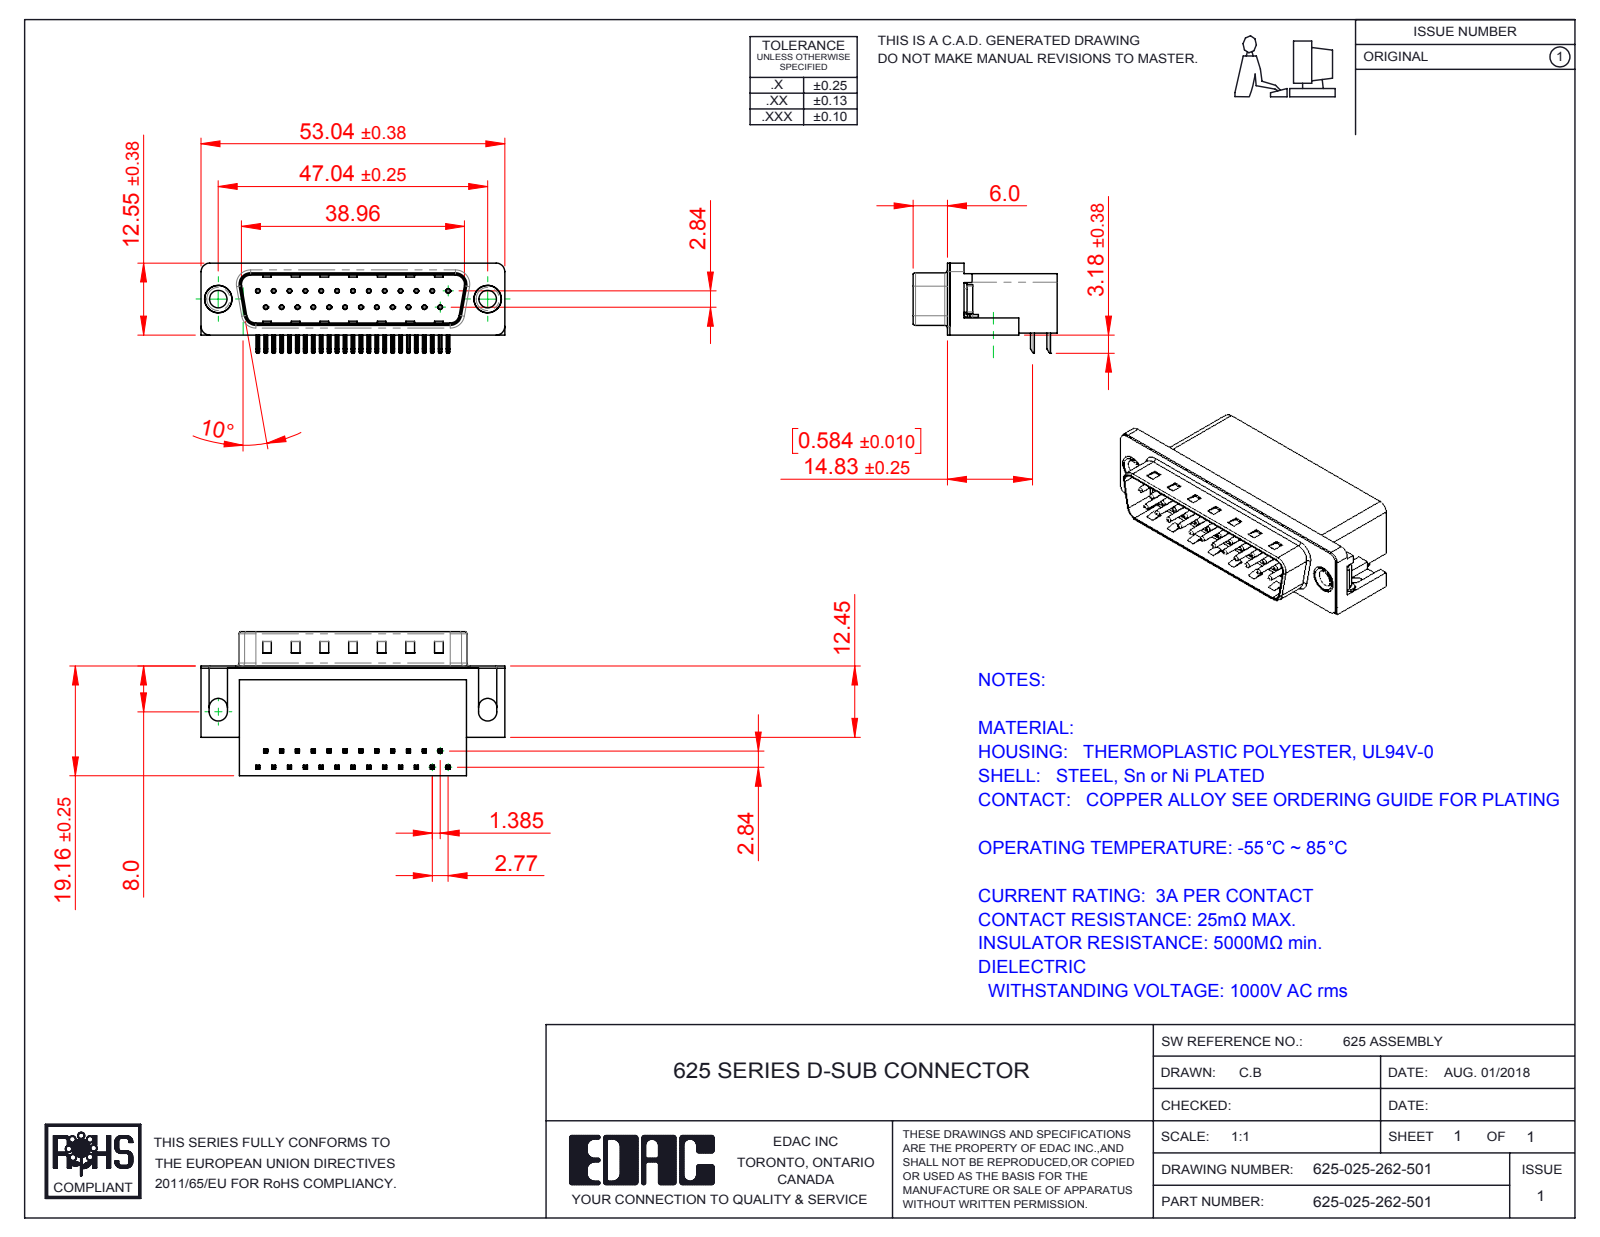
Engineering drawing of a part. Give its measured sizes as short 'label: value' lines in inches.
name: 625 Contact Bottom; 625 Thru Hole Rivet; 625 Housing_25 Socket; 625 Contact Top (+3 more)
written by: SolidWorks 2016 (CONFIG_CONTROL_DESIGN)
unit: in
bodies: 31 solids, 2223 faces (1407 planar, 639 cylindrical, 177 other)
size: 2.088 × 0.991 × 0.619
volume: 0.557 in³; area: 13.49 in²
holes: 25× ⌀0.014, 25× ⌀0.031, 2× ⌀0.12, 2× ⌀0.157, 2× ⌀0.189, 2× ⌀0.197
bosses: 25× ⌀0.03, 2× ⌀0.193, 2× ⌀0.187, 2× ⌀0.152
rounds: 108× R0.01, 50× R0.005, 16× R0.039, 9× R0.02, 8× R0.063, 7× R0.059, 4× R0.035, 4× R0.079
face distances: 0.016, 0.407, 0.739, 0.083, 0.345, 0.412, 0.428, 0.067, 0.754, 0.398
hole spacings: 0.124, 0.109, 0.436, 0.218, 0.327, 0.198, 0.545, 0.294
